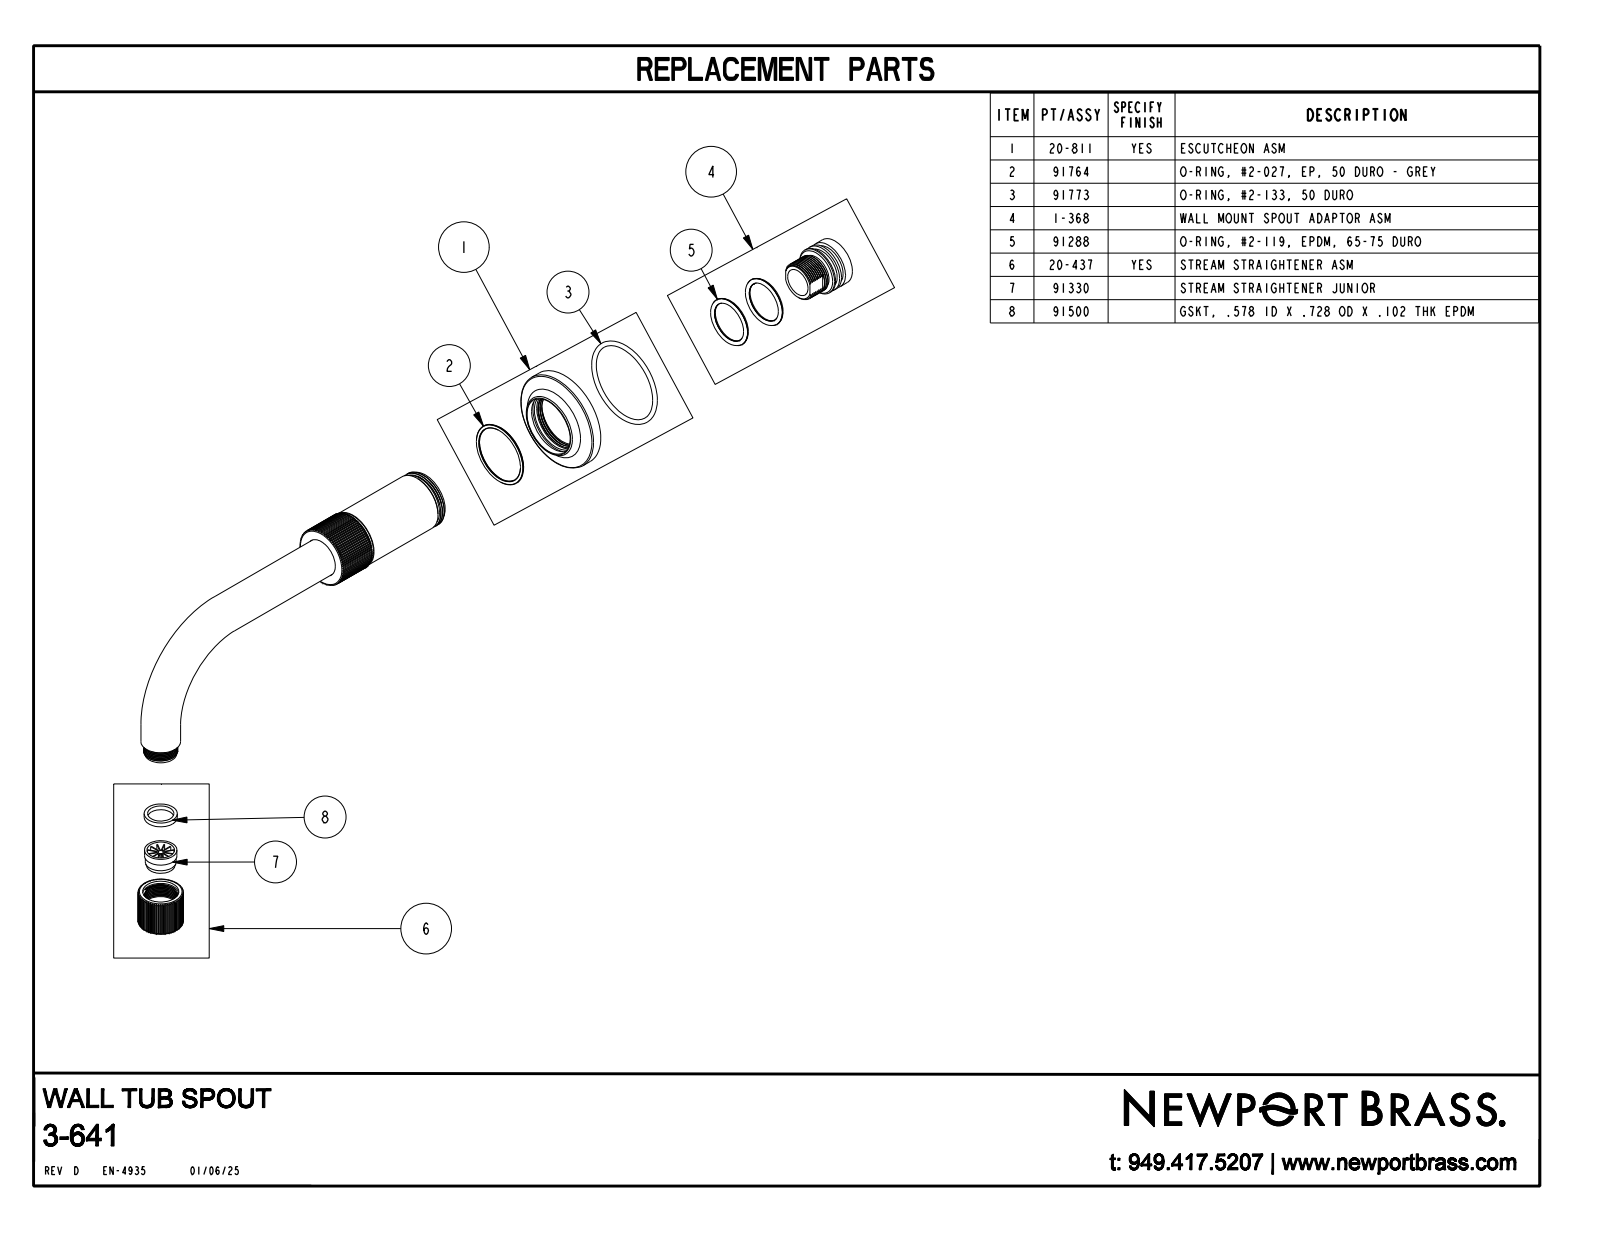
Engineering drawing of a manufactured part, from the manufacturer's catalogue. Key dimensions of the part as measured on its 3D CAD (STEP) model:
Part name (STEP PRODUCT): 3-641
STEP written by: CREO PARAMETRIC BY PTC INC, 2019352 (CONFIG_CONTROL_DESIGN)
Units: inches
Bodies: 1 solid, 565 faces (355 planar, 190 cylindrical, 20 other)
Overall size (bounding box): 8.75 × 4.385 × 2.25
Volume: 9.849 in³ · Surface area: 45.64 in²
Round holes (diameter × count): ⌀0.118 ×1, ⌀0.606 ×1, ⌀0.691 ×1
Round bosses / shafts (diameter × count): ⌀0.875 ×2, ⌀2.25 ×1, ⌀1.312 ×1, ⌀1.28 ×1, ⌀0.68 ×1, ⌀0.16 ×1
Partial cylindrical surfaces — rounded edges, fillets, slot ends (radius × count): R0.3 ×1, R0.5 ×1, R0.675 ×1
Main face-to-face distances: 0.849, 3.25, 0.848, 0.624, 0.623, 0.122, 0.624, 0.017, 0.5, 2.75
